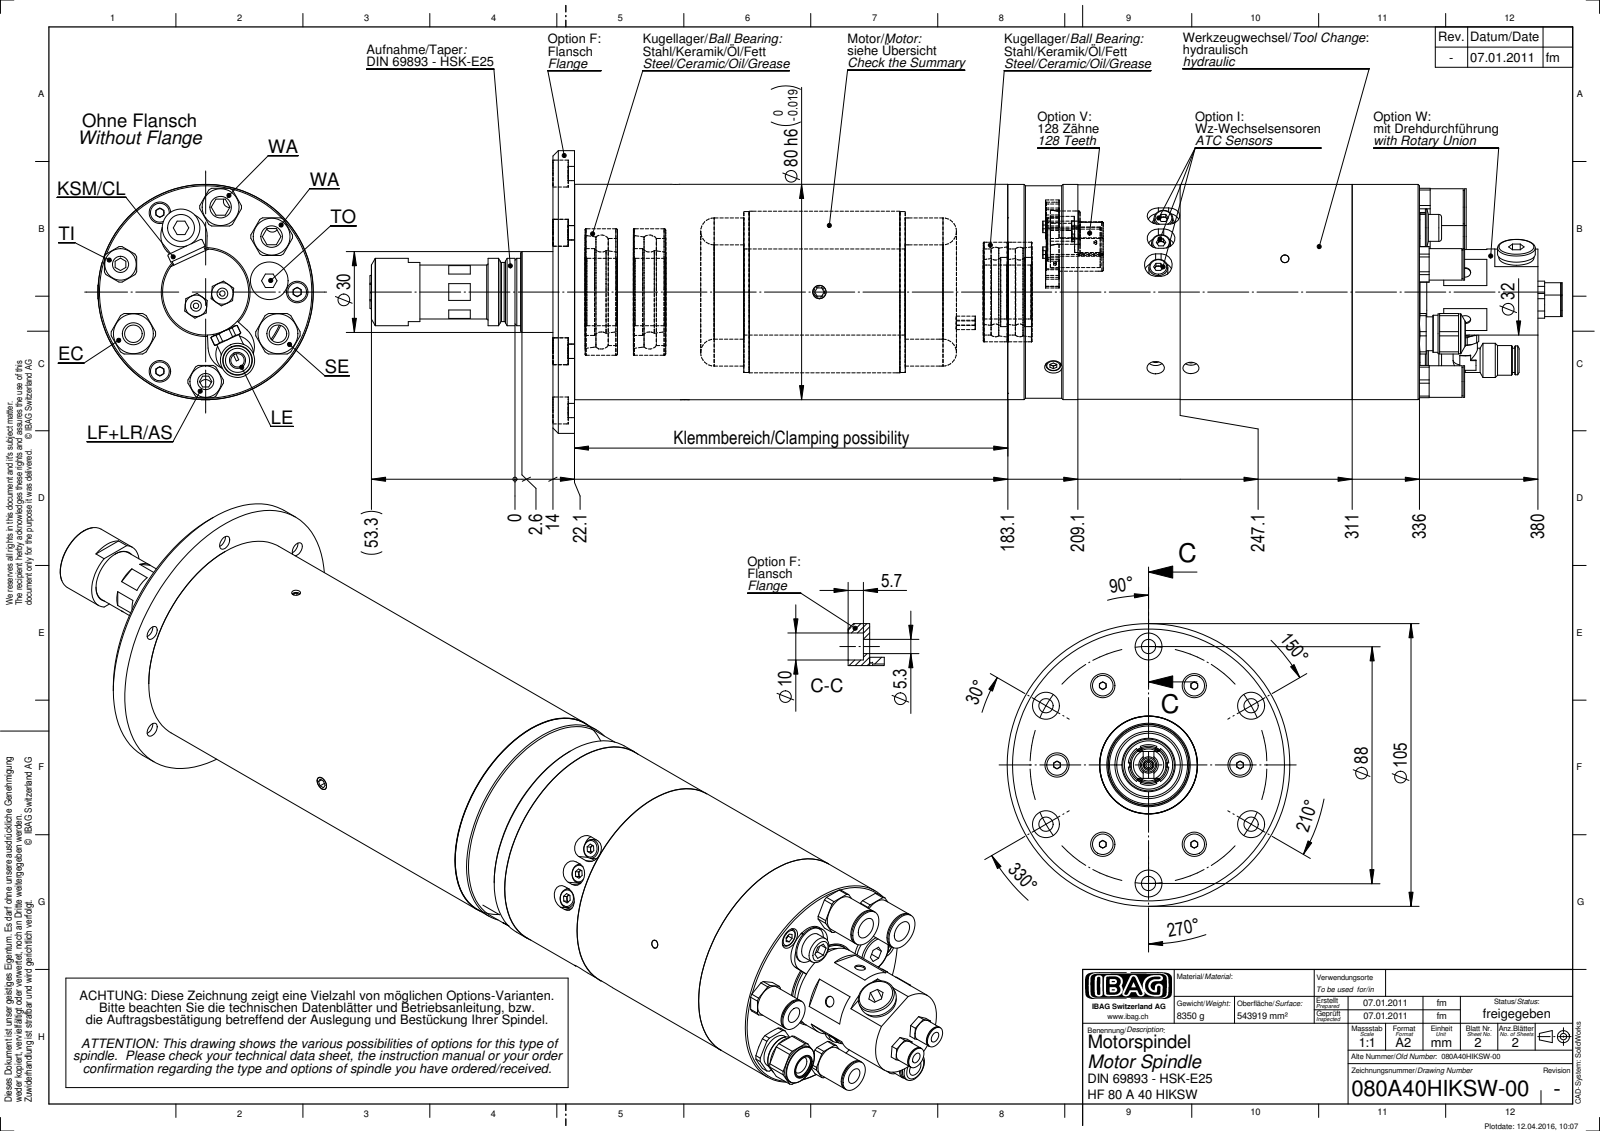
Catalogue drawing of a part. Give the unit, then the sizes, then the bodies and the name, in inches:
Units: inches
Overall size (bounding box): 17.435 × 3.15 × 3.15
Round holes (diameter × count): ⌀0.157 ×6, ⌀0.315 ×5, ⌀0.236 ×4, ⌀0.256 ×4, ⌀0.13 ×2, ⌀0.323 ×2, ⌀0.118 ×1, ⌀0.134 ×1, ⌀0.142 ×1
Round bosses / shafts (diameter × count): ⌀0.301 ×6, ⌀0.551 ×4, ⌀0.583 ×2, ⌀0.543 ×2, ⌀0.539 ×2, ⌀0.512 ×2, ⌀0.496 ×2, ⌀0.461 ×2
Partial cylindrical surfaces — rounded edges, fillets, slot ends (radius × count): R0.163 ×6, R0.335 ×4, R0.26 ×2, R0.305 ×2, R0.325 ×2, R0.118 ×1, R0.213 ×1, R1.22 ×1
Main face-to-face distances: 12.673, 11.689, 0.984, 0.315, 11.374, 12.358, 9.173, 8.858, 2.516, 3.5
Hole centre spacings: 1.339, 0.246, 0.672, 0.892, 1.003, 1.094, 1.22, 1.26
Bodies: 0 solids, 744 faces (339 planar, 251 cylindrical, 154 other)
Part name (STEP PRODUCT): 080A40HIKSW-00
STEP written by: SolidWorks 2014 (CONFIG_CONTROL_DESIGN)
